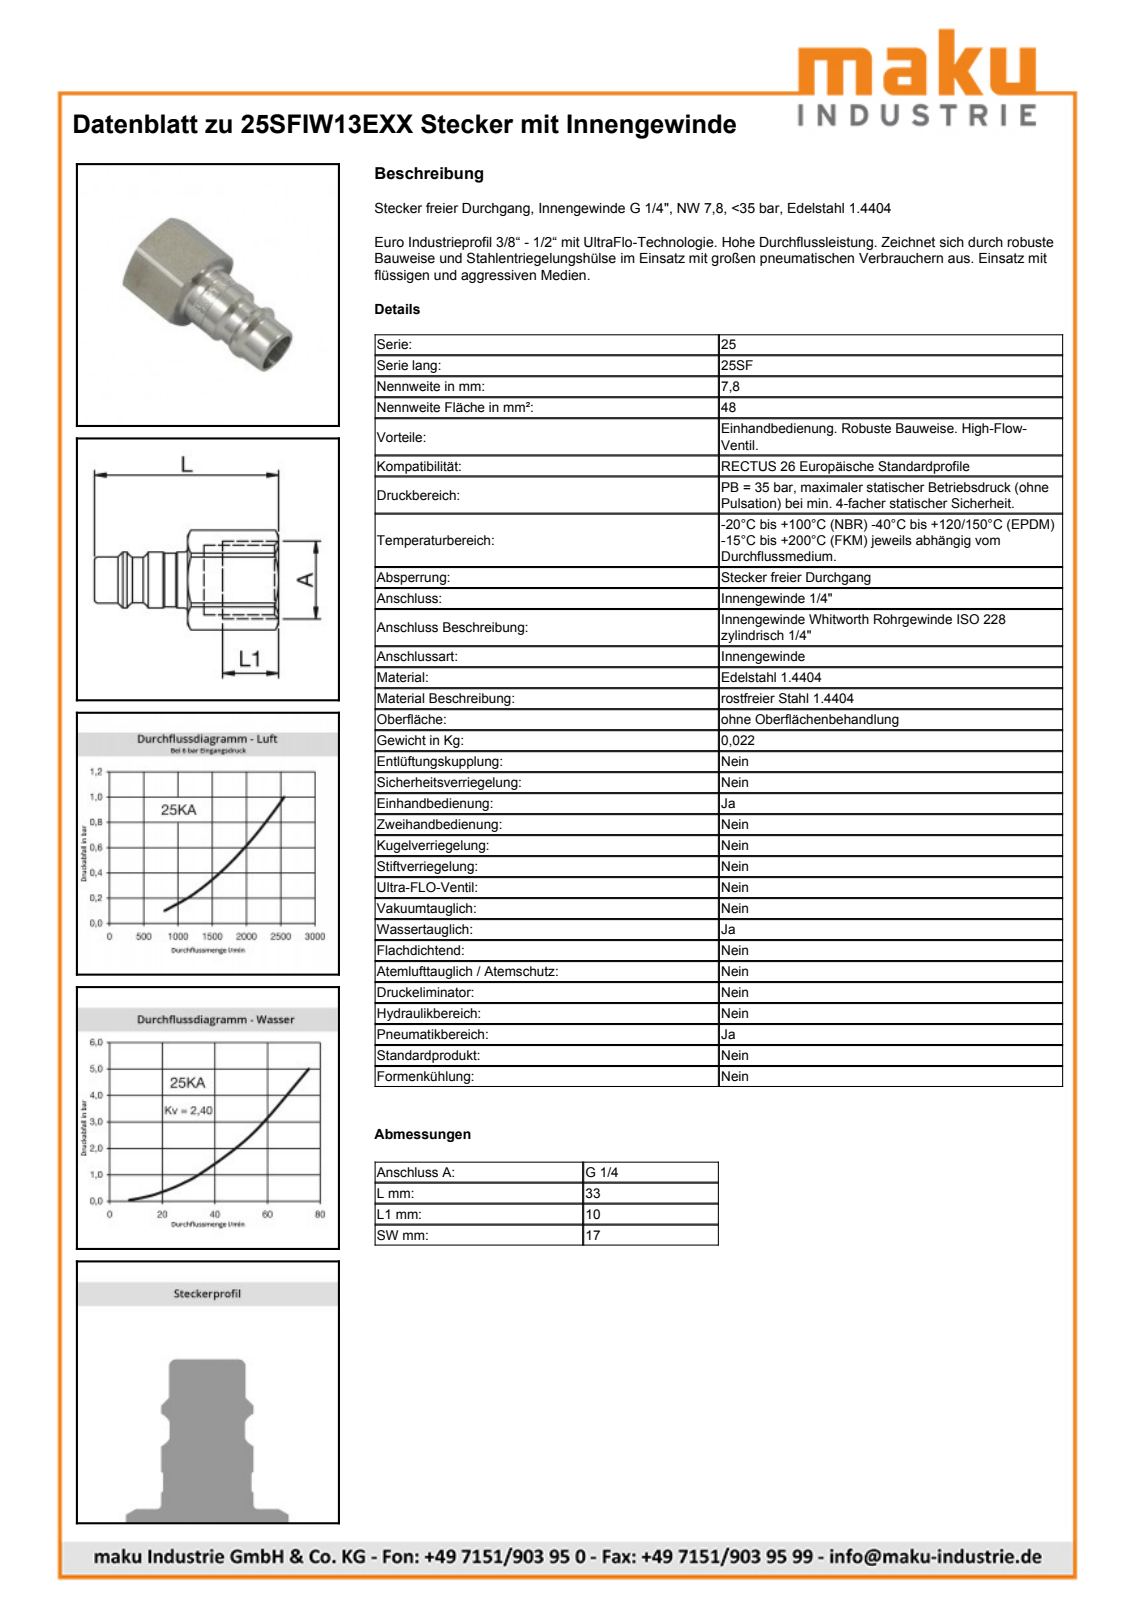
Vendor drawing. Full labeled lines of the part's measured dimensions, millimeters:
Part name (STEP PRODUCT): D105656
STEP written by: Autodesk Inventor 2011 (AUTOMOTIVE_DESIGN)
Units: millimetres
Bodies: 1 solid, 41 faces (10 planar, 12 cylindrical, 19 other)
Overall size (bounding box): 33 × 19.15 × 17
Volume: 3 004 mm³ · Surface area: 2 736 mm²
Round holes (diameter × count): ⌀7.85 ×1, ⌀11.45 ×1
Round bosses / shafts (diameter × count): ⌀12 ×1, ⌀9.9 ×1, ⌀9.75 ×1
Partial cylindrical surfaces — rounded edges, fillets, slot ends (radius × count): R9.57 ×1
Main face-to-face distances: 17, 13, 3, 10, 20, 23, 33
